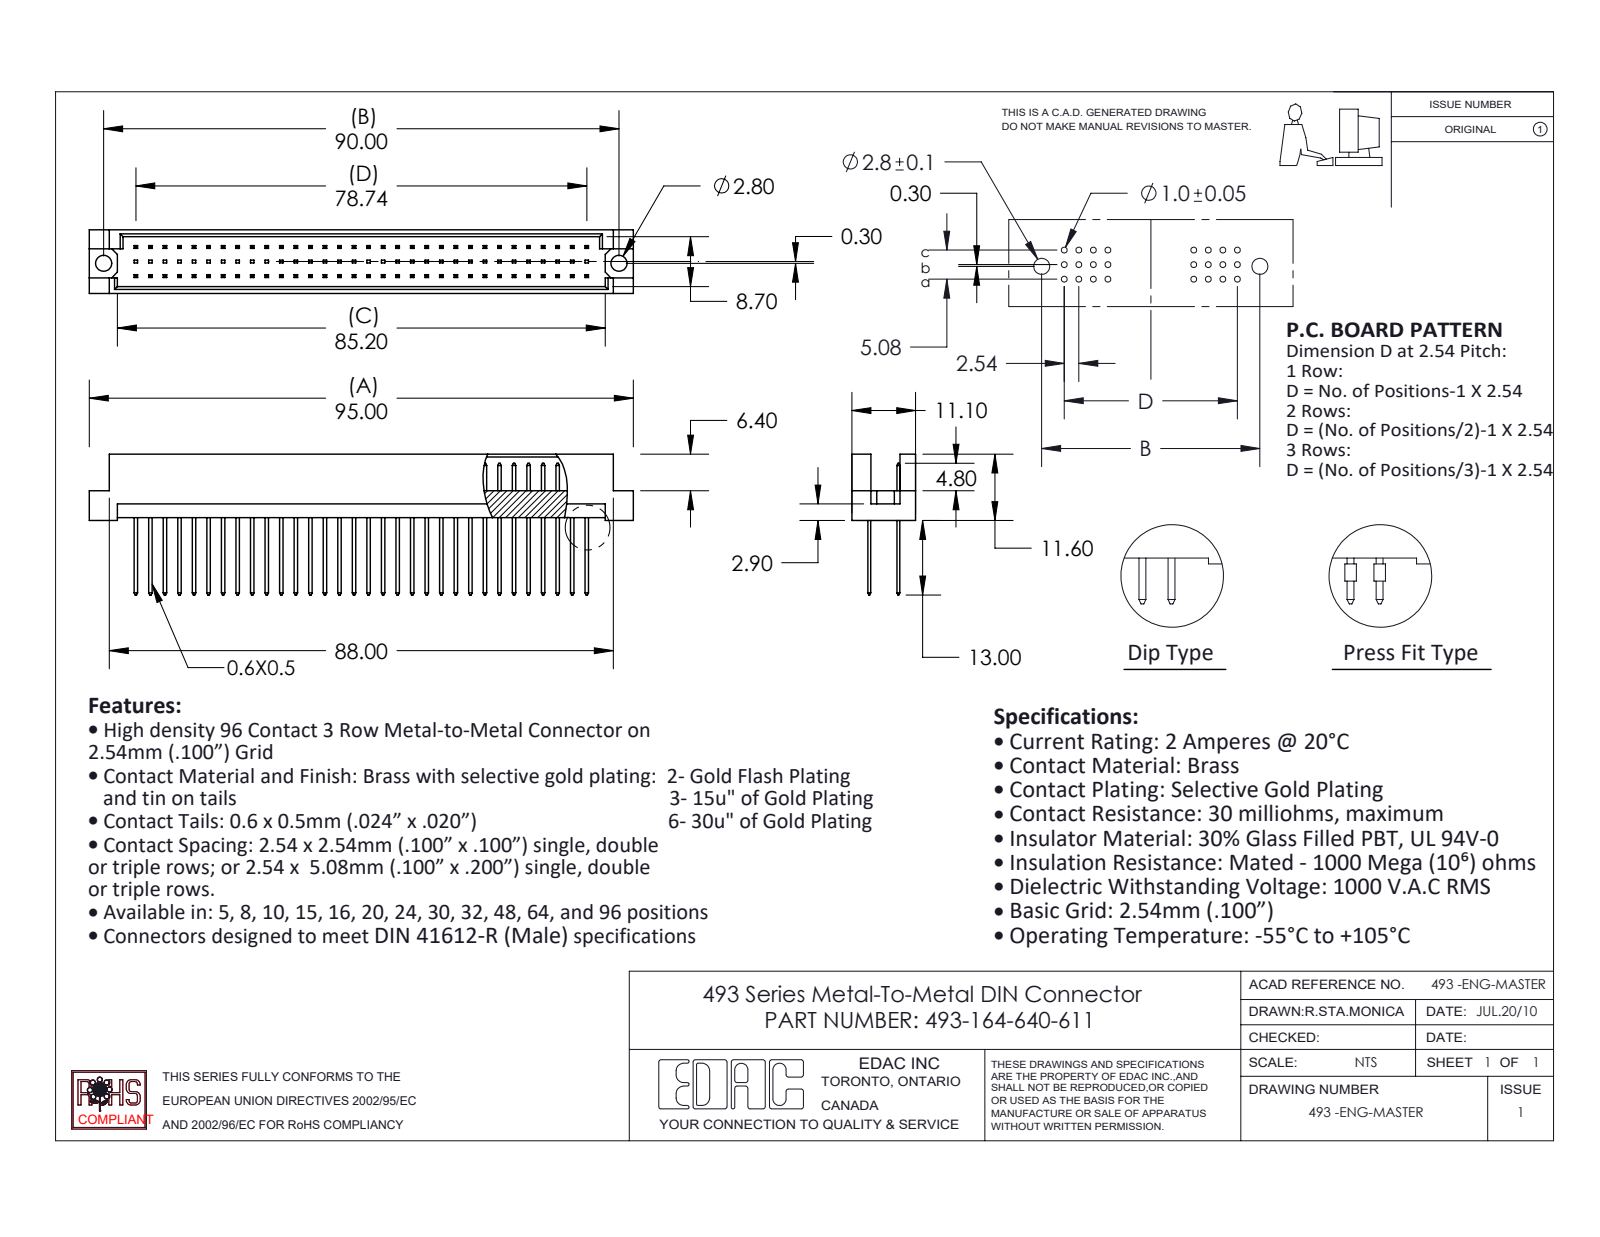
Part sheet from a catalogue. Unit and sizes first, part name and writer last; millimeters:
Units: millimetres
Overall size (bounding box): 95 × 24.6 × 11.1
Round holes (diameter × count): ⌀2.8 ×2
Main face-to-face distances: 5.08, 1.2, 9.9, 0.5, 2.76, 3.26, 7.84, 8.34, 1.56, 2.06
Hole centre spacings: 90
Volume: 6 093 mm³ · Surface area: 9 688 mm²
Bodies: 65 solids, 1332 faces (1328 planar, 4 cylindrical, 0 other)
Part name (STEP PRODUCT): 493-164-640-611; 493-290_40; 493 Part_96
STEP written by: SolidWorks 2020 (CONFIG_CONTROL_DESIGN)
